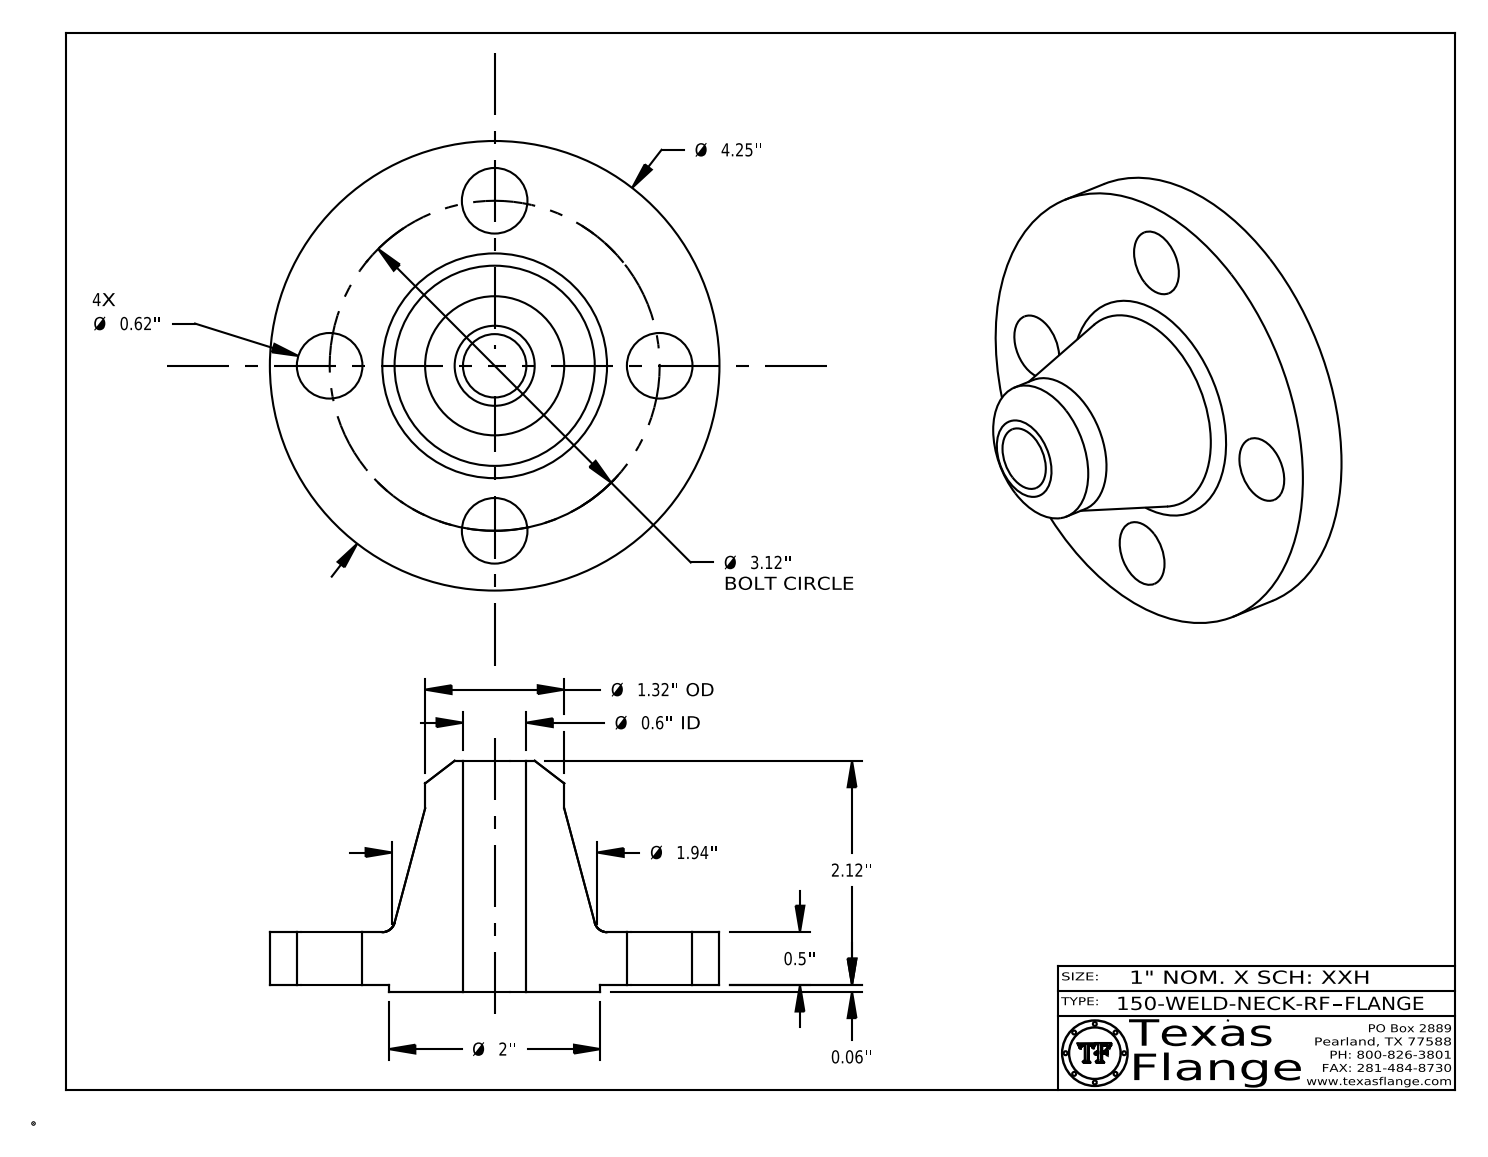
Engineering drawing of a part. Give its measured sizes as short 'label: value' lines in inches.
name: 150-WELD-NECK-RF
written by: CATIA V5 STEP AP214 (AUTOMOTIVE_DESIGN)
unit: in
bodies: 1 solid, 411 faces (369 planar, 36 cylindrical, 6 other)
size: 4.25 × 4.25 × 2.183
volume: 9.048 in³; area: 46.2 in²
holes: 4× ⌀0.62, 1× ⌀0.495, 1× ⌀0.599
bosses: 8× ⌀0.03, 1× ⌀4.25, 1× ⌀2, 1× ⌀1.315, 1× ⌀0.39
face distances: 0.5, 0.063, 0.563, 2.183, 2.12, 1.62, 0.548, 0.485, 0.015, 1.635
hole spacings: 1.56, 2.206, 1.194, 2.882, 3.12, 1.56
